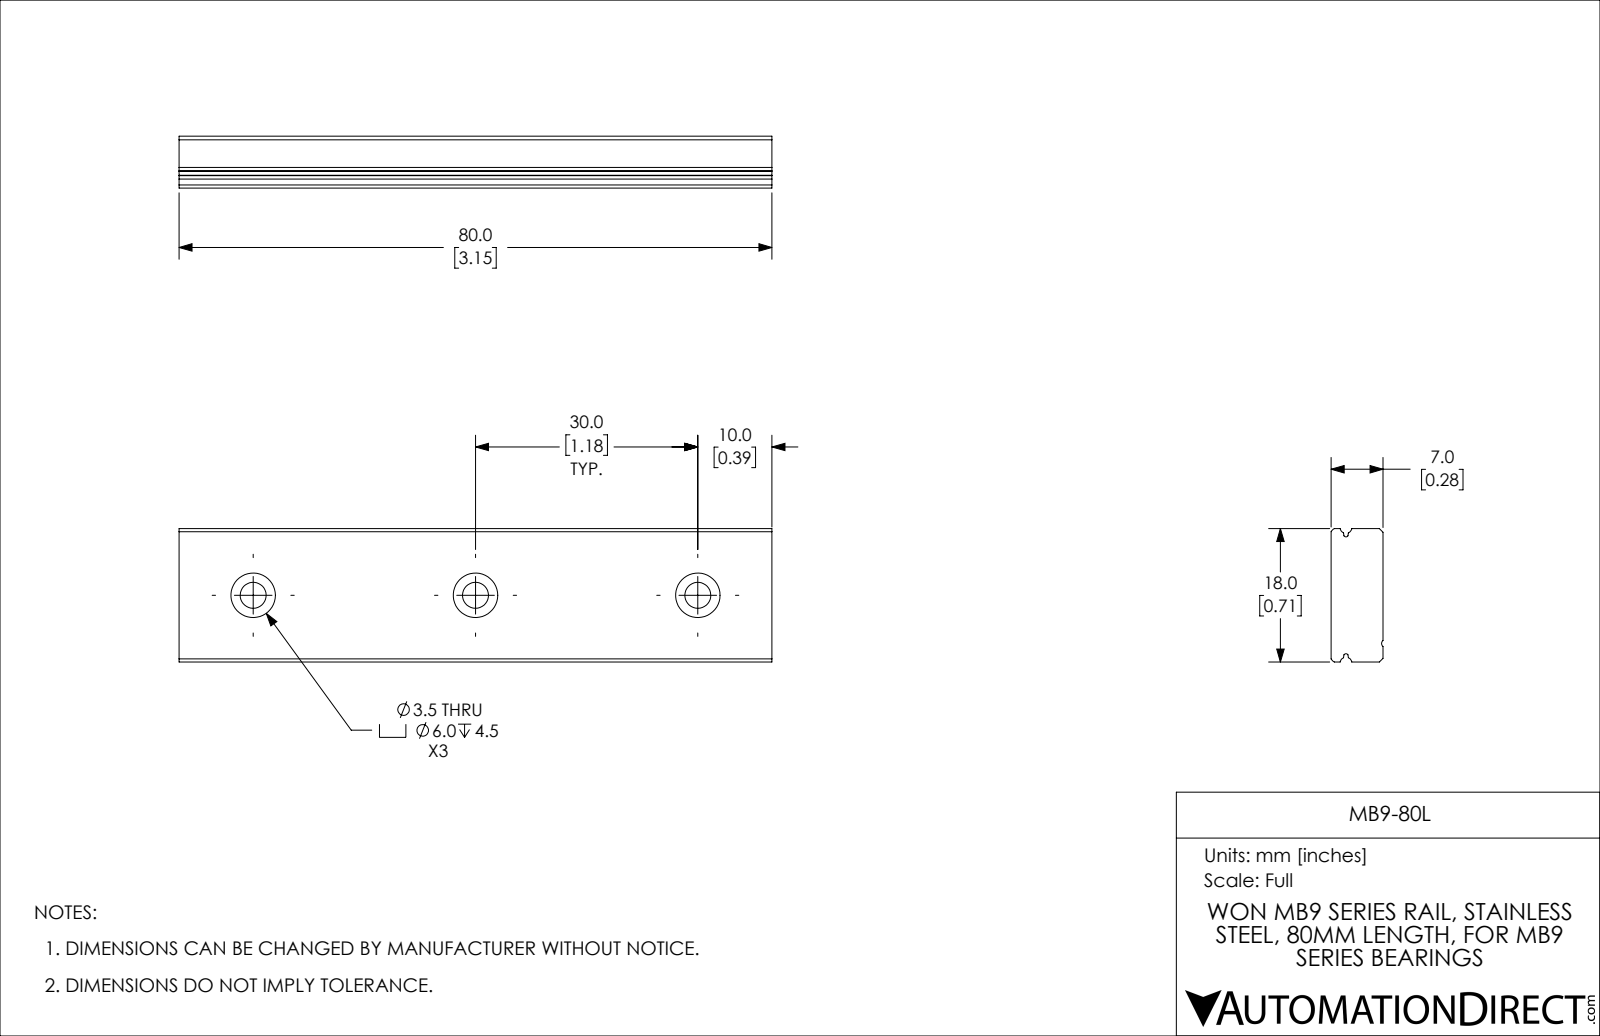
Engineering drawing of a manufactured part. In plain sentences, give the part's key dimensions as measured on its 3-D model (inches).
The part is named "MB9-80L". Its 3-D file was written by "SolidWorks 2019 (CONFIG_CONTROL_DESIGN)". It is 1 solid with 40 faces: 18 planar, 22 cylindrical and 0 other. Overall it measures 3.15 by 0.709 by 0.276 inches. Its volume is 0.575 cubic inches and its surface area 7.248 square inches. Round holes: 3 of diameter 0.138, 3 of diameter 0.236. Partial cylindrical surfaces (rounded edges, fillets, slot ends): 2 of radius 0.013, 2 of radius 0.031, 2 of radius 0.037, 1 of radius 0.02. The main face-to-face distances are 0.276, 0.709, 3.15, 0.064, 0.098, 0.177. The hole center spacings are 1.181, 2.362.
